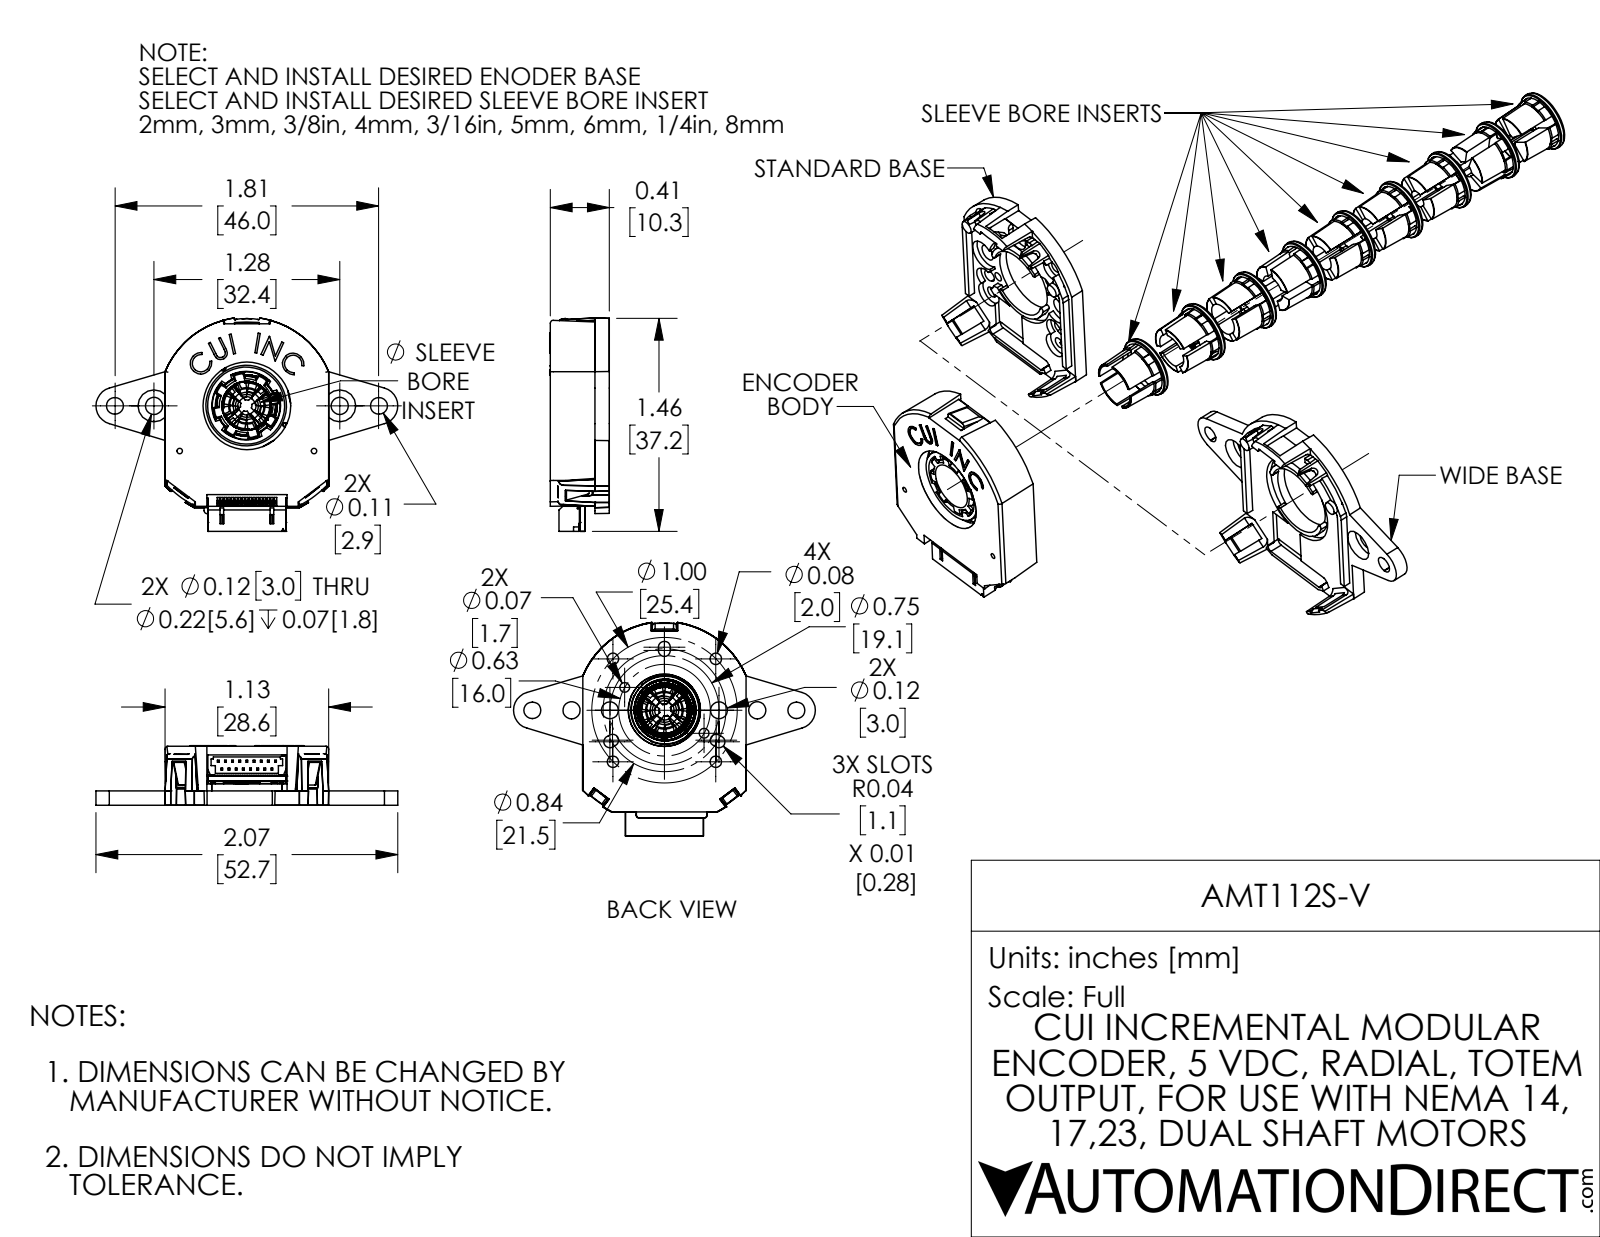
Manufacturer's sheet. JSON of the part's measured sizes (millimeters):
{"part_name": "AMT112S-V", "step_written_by": "SolidWorks 2021 (AUTOMOTIVE_DESIGN)", "units": "millimeters", "bodies": {"solids": 16, "faces": 4202, "planar": 1922, "cylindrical": 1559, "other": 721}, "overall_size": [138.8, 116.2, 37.3], "volume_mm3": 9240, "surface_area_mm2": 16890, "round_holes": [[0.7, 168], [0.8, 4], [0.9, 4], [2, 4], [0.8, 2], [1.6, 2], [1.7, 2], [2.3, 2], [2.9, 2], [3, 2], [4.1, 2], [4.5, 2]], "round_bosses_or_shafts": [[1.5, 4], [1.3, 4], [10.5, 2], [2.4, 2], [19.4, 1], [11.8, 1], [9, 1]], "partial_cylinders_radius": [[9.6, 64], [1, 30], [12.6, 29], [2, 11], [0.4, 8], [0.5, 6], [1, 6], [0.3, 4]], "face_to_face_distances": [1.4, 0.8, 2.5, 39.3, 40.1, 40.7, 41.6, 42.8, 4, 36.8], "hole_center_spacings": [9.3, 7.1, 4.6, 7.8, 7.1, 1.7, 2.5, 5.7]}
